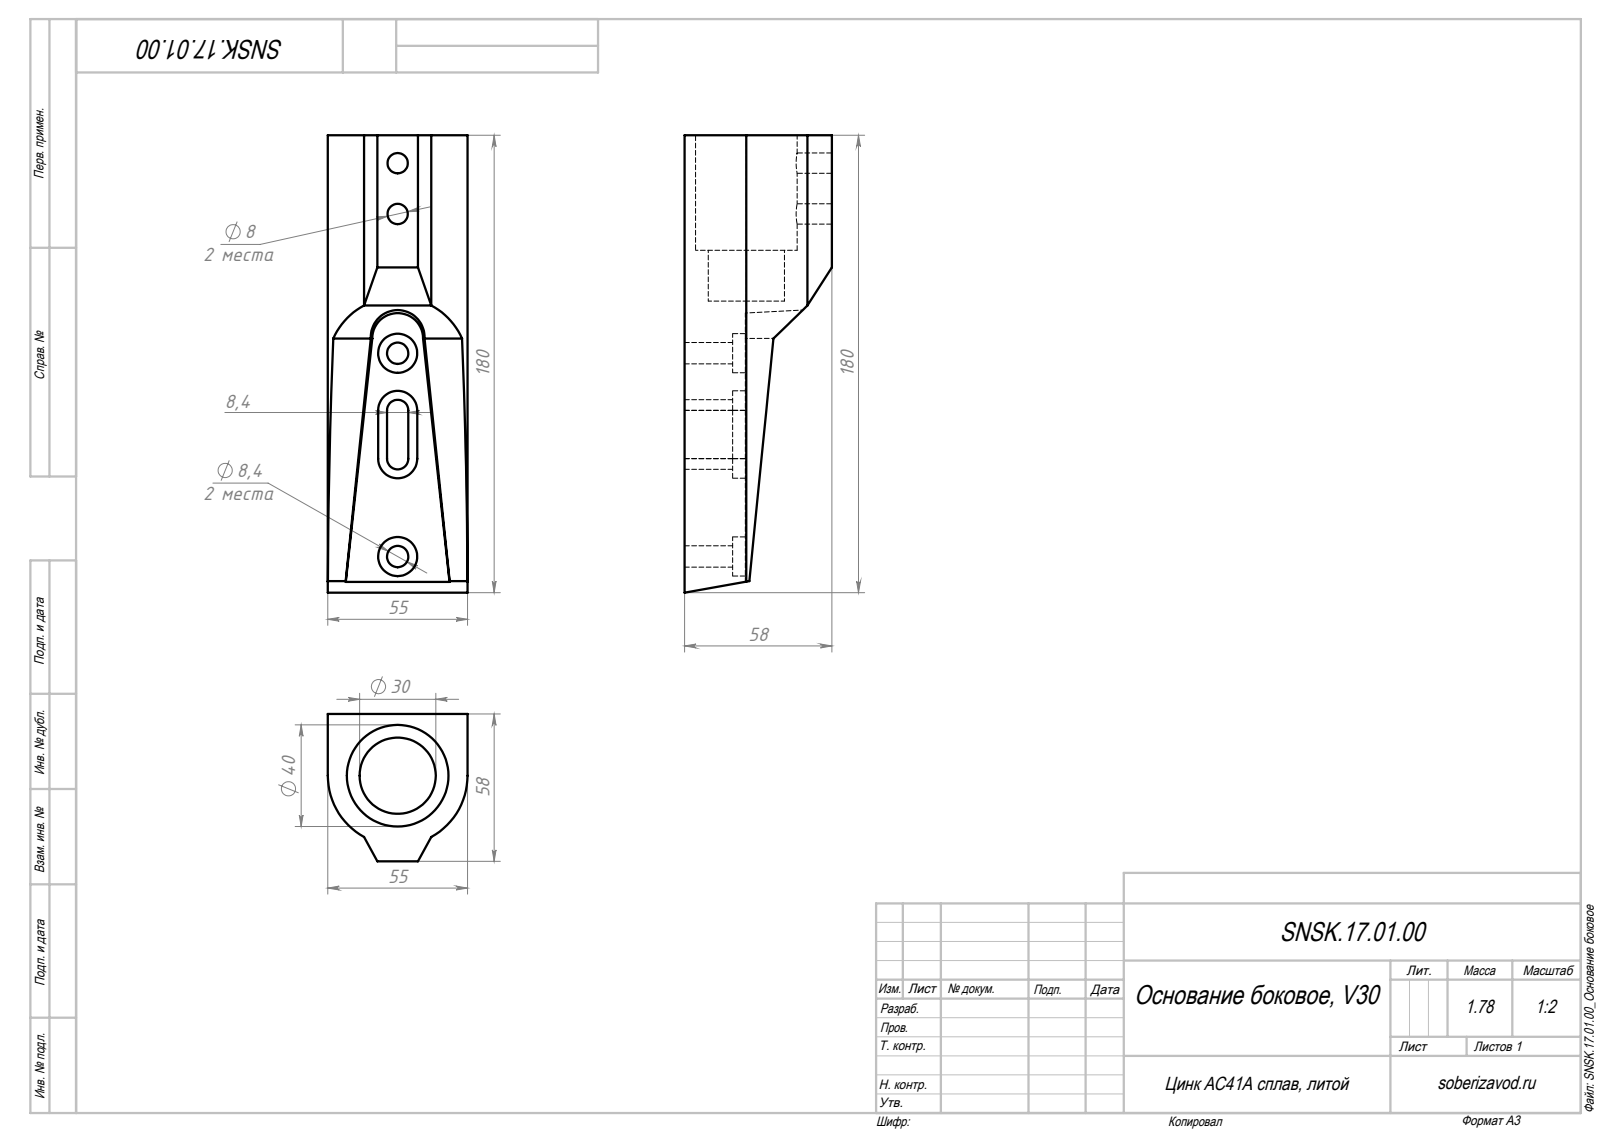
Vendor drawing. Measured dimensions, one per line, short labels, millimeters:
written by: SolidWorks 2016 (AUTOMOTIVE_DESIGN)
unit: mm
bodies: 1 solid, 50 faces (24 planar, 24 cylindrical, 2 other)
size: 180 × 58 × 55
volume: 265 033 mm³; area: 48 767 mm²
holes: 2× ⌀8, 2× ⌀8.4, 2× ⌀15.4, 1× ⌀30, 1× ⌀40
rounds: 2× R4.2, 2× R7.7, 1× R27.5
face distances: 55, 23.9, 58, 34.1, 23.3, 31.7, 65.3, 45.3, 20, 18.9
hole spacings: 20, 54.8, 74.8, 80, 134.8, 154.8
